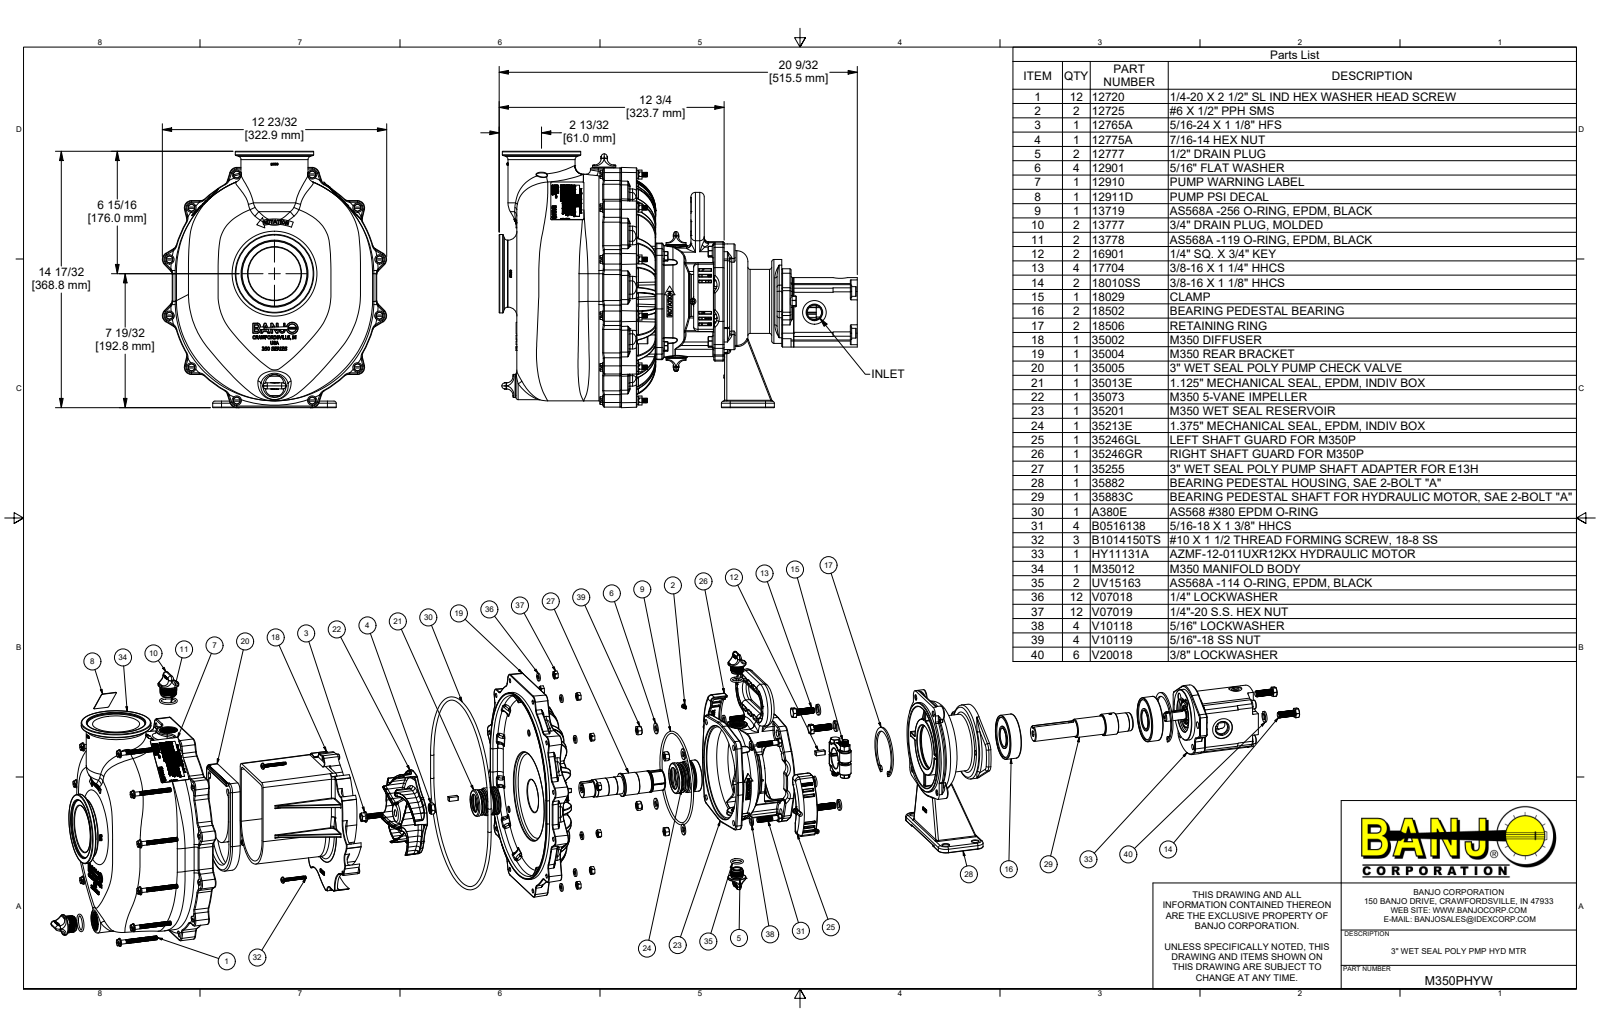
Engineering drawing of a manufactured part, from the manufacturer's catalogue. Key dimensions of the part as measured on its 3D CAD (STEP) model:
Part name (STEP PRODUCT): M350PHYW; 17704; 18010SS; 35073 (+8 more)
STEP written by: Autodesk Inventor 2022 (AUTOMOTIVE_DESIGN)
Units: inches
Bodies: 117 solids, 25622 faces (8815 planar, 4267 cylindrical, 12540 other)
Overall size (bounding box): 20.295 × 14.518 × 12.712
Volume: 443.3 in³ · Surface area: 2 951 in²
Round holes (diameter × count): ⌀0.196 ×12, ⌀0.252 ×12, ⌀0.27 ×12, ⌀0.52 ×10, ⌀0.236 ×8, ⌀0.385 ×8, ⌀0.307 ×6, ⌀0.433 ×6, ⌀0.098 ×5, ⌀0.437 ×5, ⌀0.252 ×4, ⌀0.313 ×4
Round bosses / shafts (diameter × count): ⌀0.324 ×110, ⌀0.337 ×46, ⌀0.489 ×12, ⌀0.25 ×12, ⌀0.687 ×8, ⌀0.375 ×8, ⌀0.394 ×5, ⌀0.713 ×4
Partial cylindrical surfaces — rounded edges, fillets, slot ends (radius × count): R0.031 ×309, R0.062 ×195, R0.125 ×88, R0.016 ×75, R0.094 ×69, R0.03 ×54, R0.25 ×52, R0.375 ×47
Main face-to-face distances: 0.4, 6.4, 0.5, 0.9, 5.014, 4.05, 0.269, 6.669, 1.386, 0.986
Hole centre spacings: 6.005, 3.182, 9.407, 2.594, 3.611, 5.107, 5.303, 6.137
